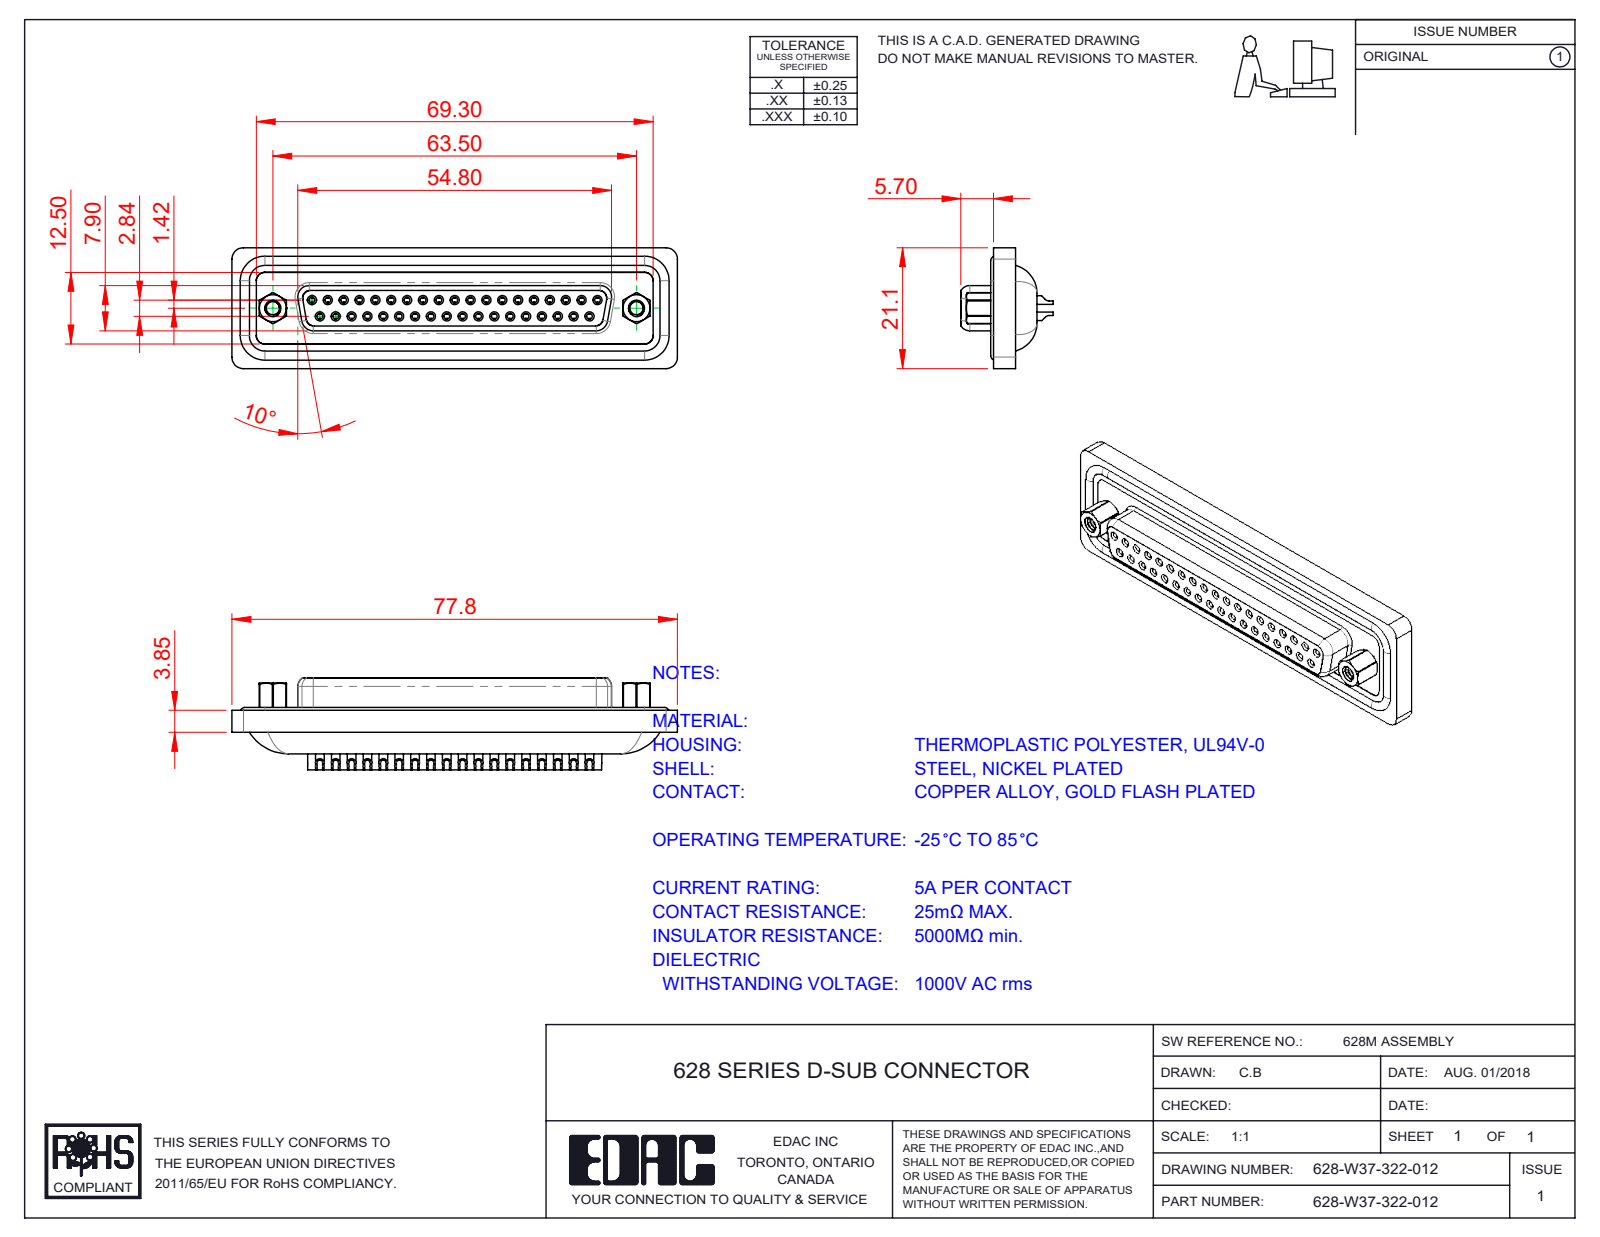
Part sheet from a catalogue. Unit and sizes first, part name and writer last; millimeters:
Units: millimetres
Overall size (bounding box): 77.8 × 21.1 × 16.1
Round holes (diameter × count): ⌀1 ×37, ⌀1.1 ×37, ⌀1.5 ×37, ⌀1.7 ×37, ⌀1.8 ×37, ⌀2 ×37, ⌀2.26 ×2, ⌀2.29 ×2, ⌀4 ×2, ⌀4.8 ×2, ⌀5 ×2
Round bosses / shafts (diameter × count): ⌀1.6 ×41, ⌀2.2 ×37, ⌀1.5 ×8, ⌀4.9 ×2, ⌀2.79 ×2
Partial cylindrical surfaces — rounded edges, fillets, slot ends (radius × count): R2 ×16, R1.5 ×14, R1.35 ×8, R2.7 ×6, R0.5 ×4, R0.9 ×4, R1.6 ×4, R1.75 ×4
Main face-to-face distances: 0.4, 7.45, 7.5, 8.45, 6.2, 13.65, 4.1, 1.1, 2.75, 8
Hole centre spacings: 3.16, 2.77, 5.54, 8.31, 5.04, 7.49, 11.08, 13.85
Volume: 11 076 mm³ · Surface area: 18 089 mm²
Bodies: 45 solids, 2532 faces (730 planar, 1071 cylindrical, 731 other)
Part name (STEP PRODUCT): 628W Contact Row 2_22; 628W Housing_37 Contacts; 628-W37-322-012; 628W Contact Row 1_22 (+4 more)
STEP written by: SolidWorks 2020 (CONFIG_CONTROL_DESIGN)
